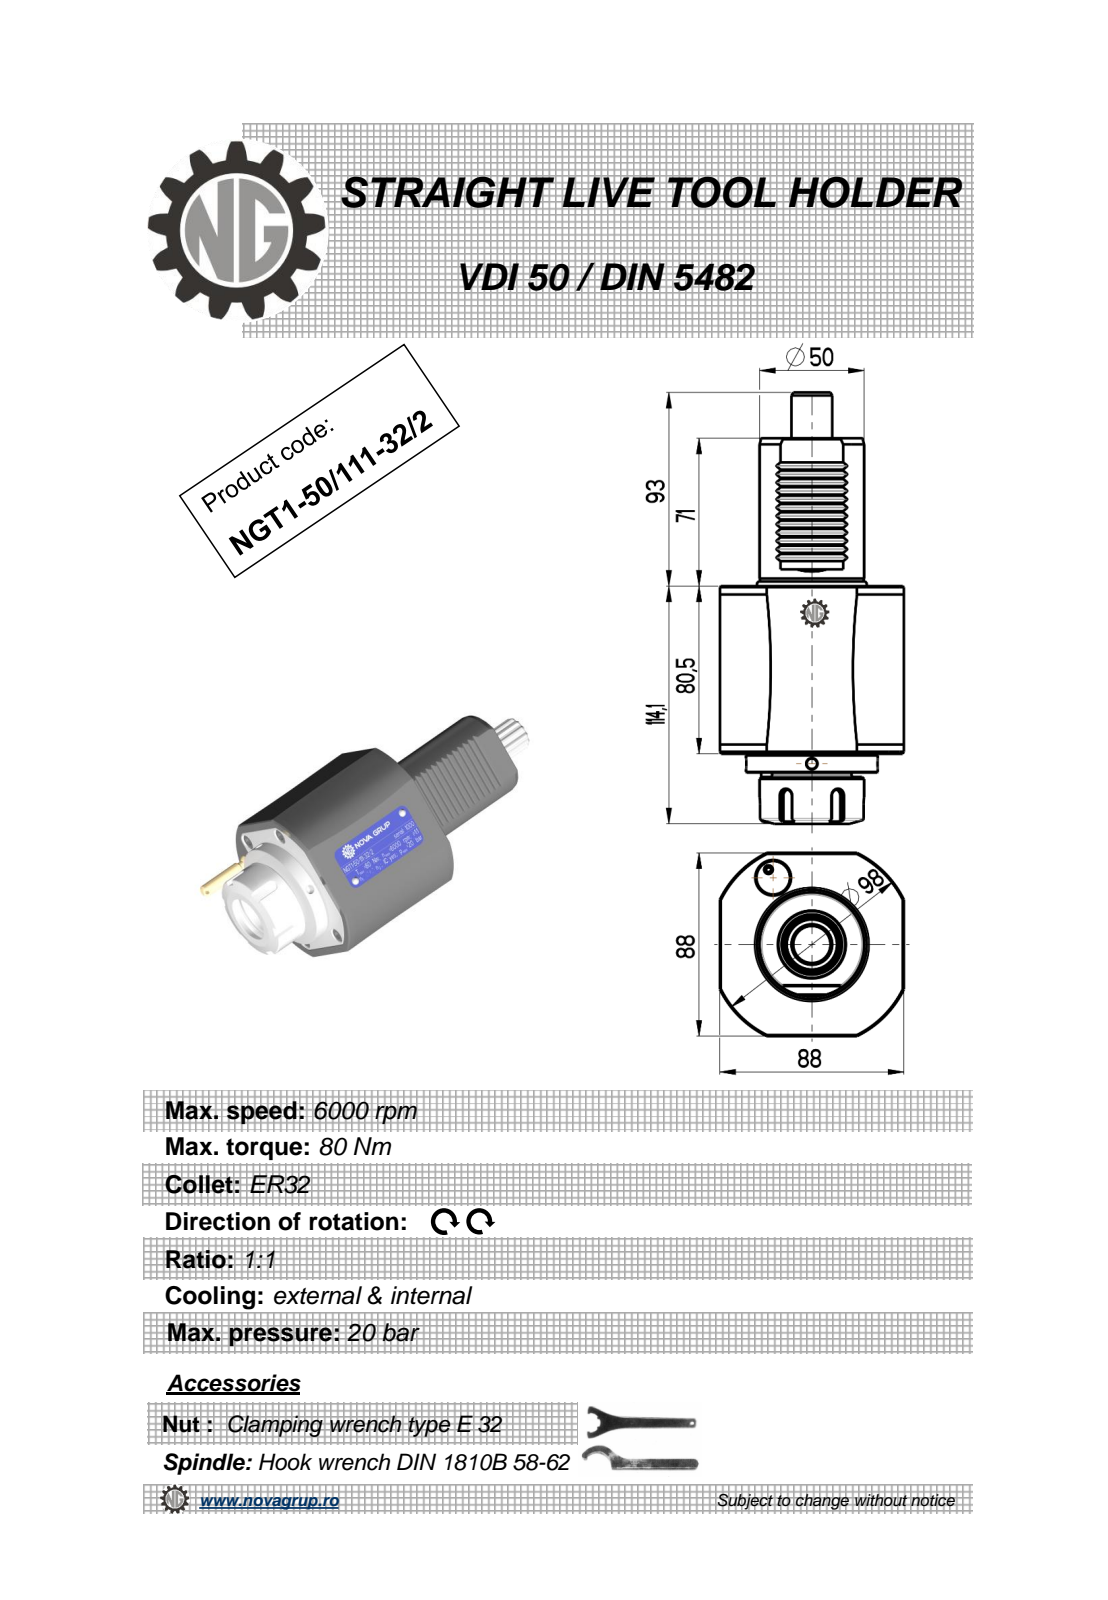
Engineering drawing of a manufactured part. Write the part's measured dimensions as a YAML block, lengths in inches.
part_name: "NGT1_50_111_32_1"
step_written_by: "PRO/ENGINEER BY PARAMETRIC TECHNOLOGY CORPORATION, 2010280 (CONFIG_CONTROL_DESIGN)"
units: inches
bodies: {solids: 1, faces: 315, planar: 102, cylindrical: 105, other: 108}
overall_size: [8.154, 3.465, 3.465]
volume: 46.52
surface_area: 96.46
round_holes:
  - {diameter: 0.197, count: 2}
  - {diameter: 0.098, count: 1}
  - {diameter: 0.118, count: 1}
  - {diameter: 1.063, count: 1}
round_bosses_or_shafts:
  - {diameter: 2.48, count: 1}
  - {diameter: 2.012, count: 1}
  - {diameter: 1.969, count: 1}
  - {diameter: 1.614, count: 1}
  - {diameter: 0.354, count: 1}
  - {diameter: 0.276, count: 1}
  - {diameter: 0.197, count: 1}
partial_cylinders:
  - {radius: 0.131, count: 24}
  - {radius: 0.012, count: 12}
  - {radius: 0.118, count: 5}
  - {radius: 0.325, count: 1}
  - {radius: 0.384, count: 1}
  - {radius: 1.929, count: 1}
face_to_face_distances: [3.465, 3.169, 0.354, 3.524, 2.795, 5.965, 6.319, 0.111, 3.189, 5.984]
hole_center_spacings: [1.634]
